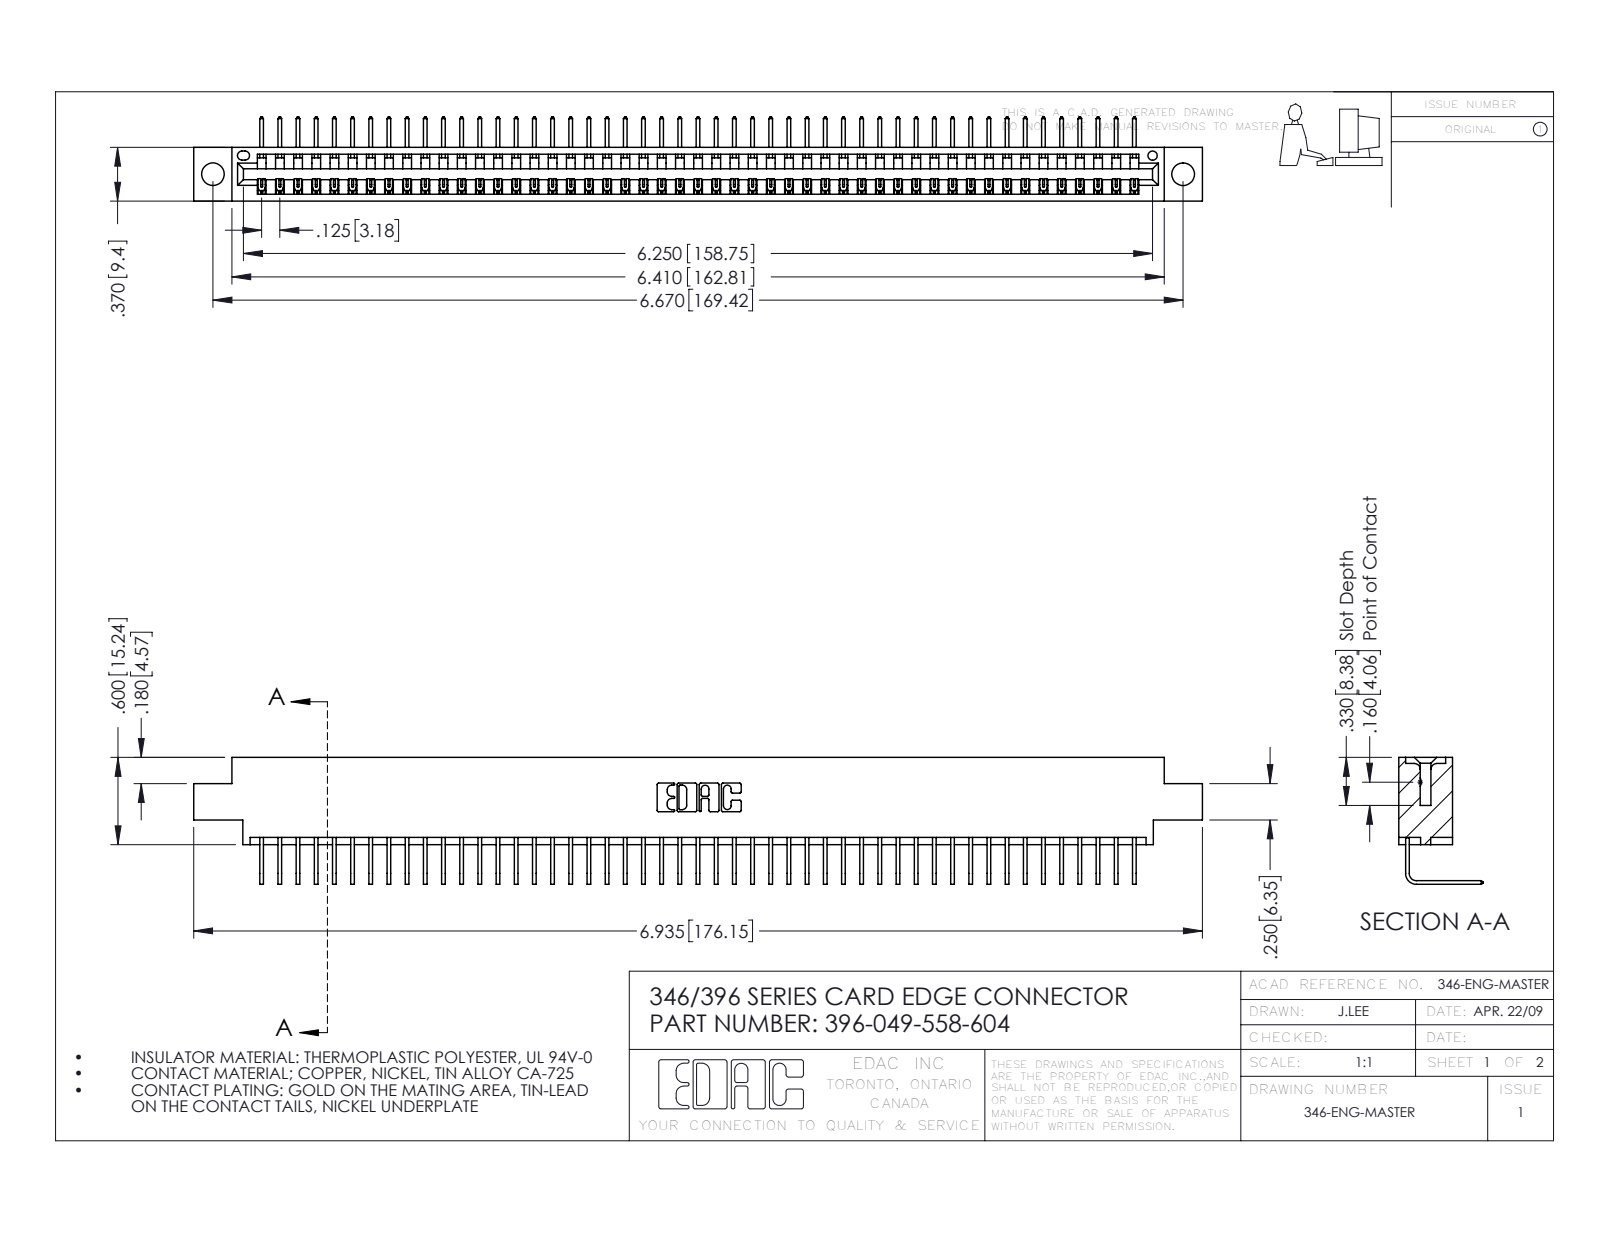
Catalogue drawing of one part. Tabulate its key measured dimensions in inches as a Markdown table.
| quantity | value |
| --- | --- |
| part name | 396-049-558-604; 345-292-001_558 Tail - 2; 346 Part_0.170 Offset - 0.156 Dia-TH |
| STEP written by | SolidWorks 2016 (CONFIG_CONTROL_DESIGN) |
| units | inches |
| bodies | 50 solids, 3066 faces (2138 planar, 928 cylindrical, 0 other) |
| overall size | 6.935 × 0.873 × 0.58 |
| volume | 1.027 in³ |
| surface area | 34.18 in² |
| round holes (diameter × count) | 0.156 × 2, 0.064 × 1 |
| partial cylindrical surfaces (radius × count) | 0.006 × 98, 0.01 × 22, 0.007 × 6, 0.031 × 6, 0.026 × 3, 0.031 × 2, 0.04 × 2, 0.014 × 1 |
| main face-to-face distances | 0.322, 0.048, 0.37, 0.25, 0.298, 0.025, 0.072, 0.148, 0.222, 0.1 |
| hole center spacings | 0.246, 6.461, 6.67 |
